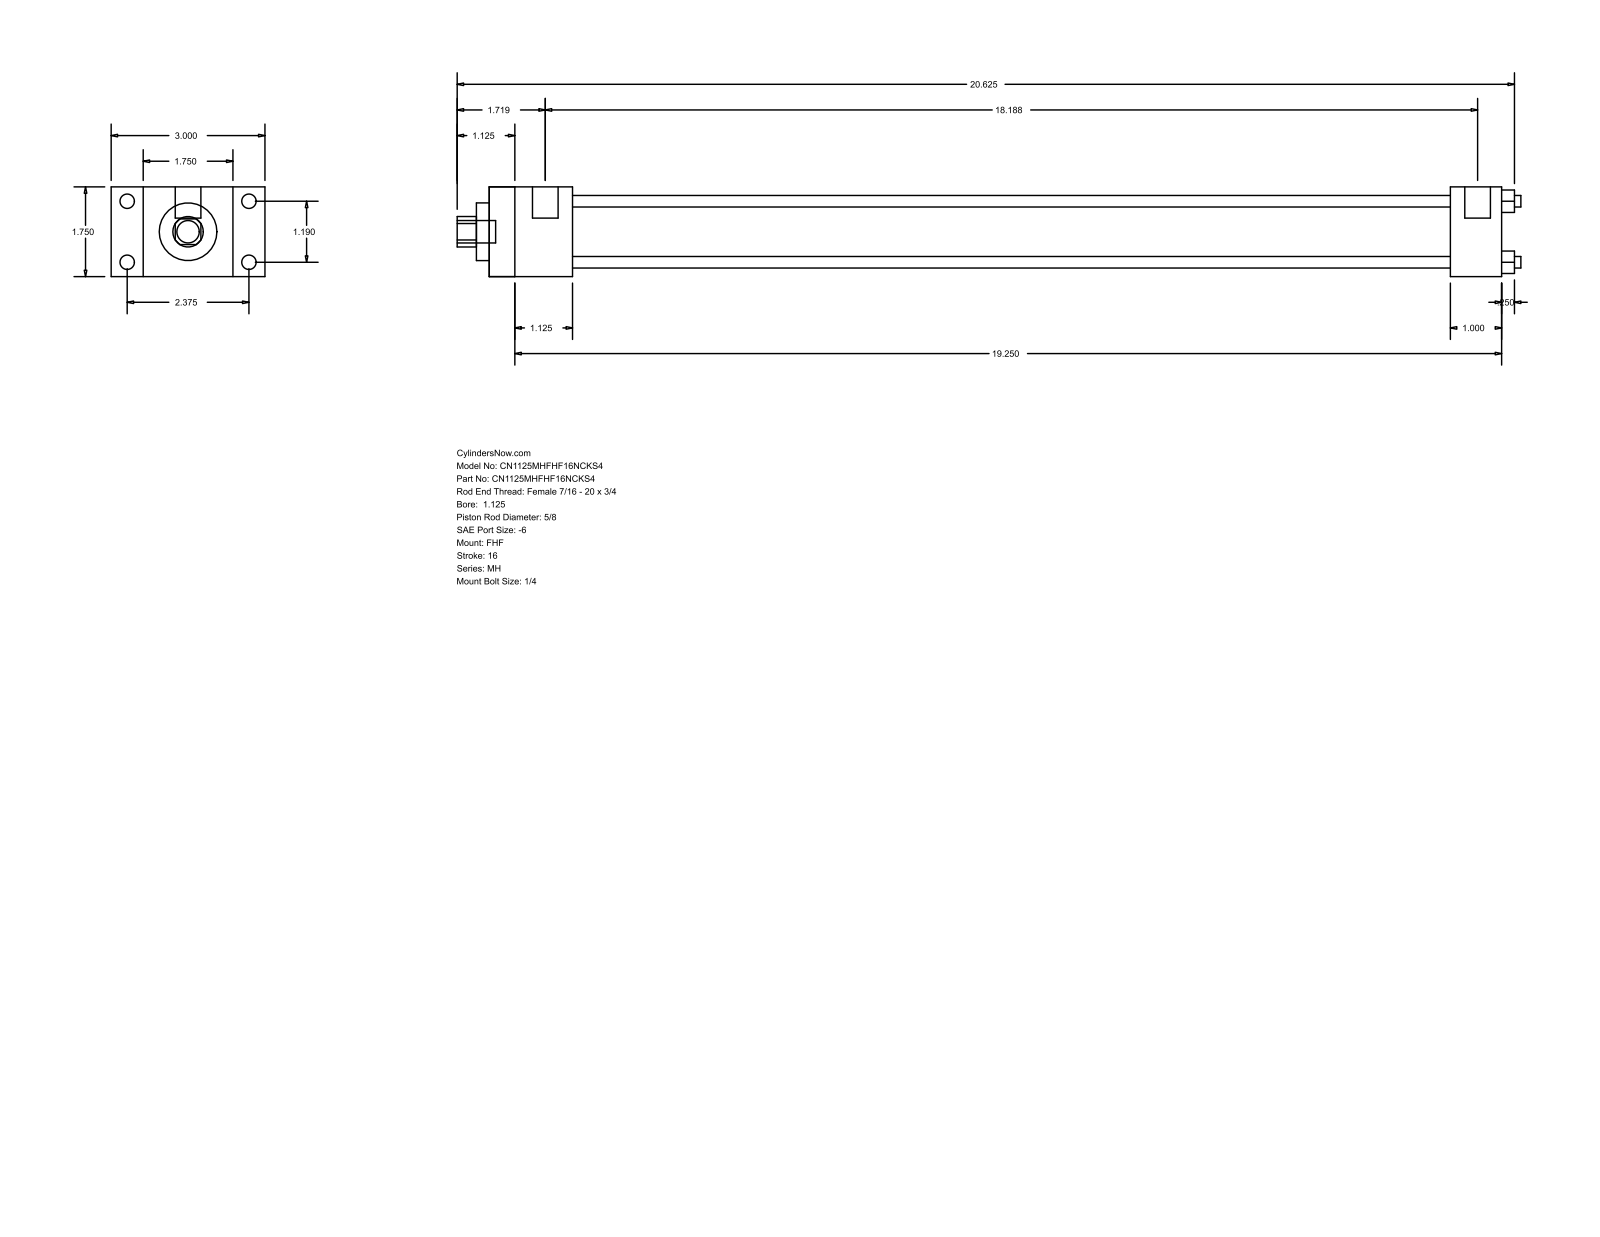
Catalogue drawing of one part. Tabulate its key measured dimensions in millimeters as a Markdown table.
| quantity | value |
| --- | --- |
| part name | MH_FHF__0112_0.625 |
| STEP written by | GSSL Pune (CONFIG_CONTROL_DESIGN) |
| units | millimeters |
| bodies | 0 solids, 88 faces (60 planar, 28 cylindrical, 0 other) |
| overall size | 527.05 × 76.2 × 44.45 |
| round holes (diameter × count) | 5.71 × 4, 15.88 × 1, 28.57 × 1, 34.92 × 1 |
| round bosses / shafts (diameter × count) | 7.14 × 4, 5.56 × 4, 12.7 × 2, 11.11 × 1 |
| partial cylindrical surfaces (radius × count) | 7.54 × 1 |
| main face-to-face distances | 44.46, 15.87, 60.33, 41.27, 76.2, 501.64, 460.37, 476.24, 434.97, 25.4 |
| hole center spacings | 21.37, 30.22, 42.74 |
